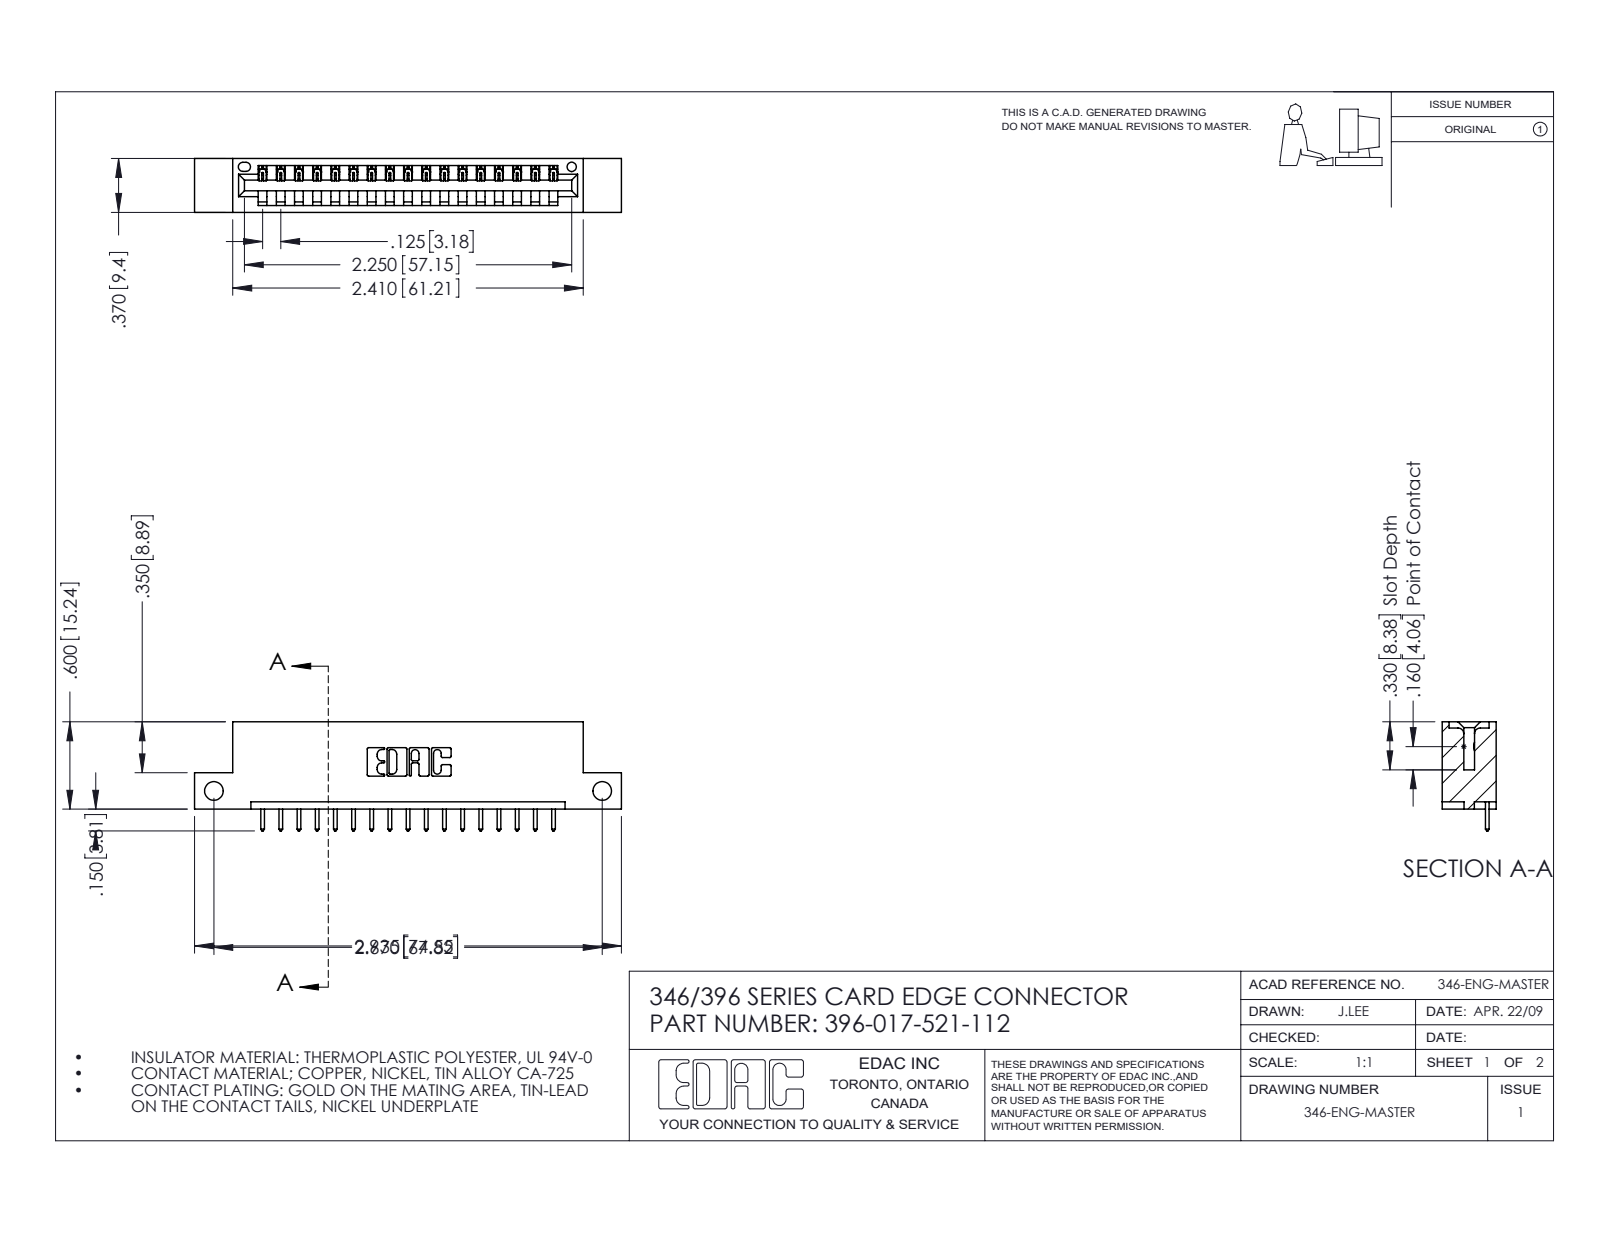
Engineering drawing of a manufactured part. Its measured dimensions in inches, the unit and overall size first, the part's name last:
Units: inches
Overall size (bounding box): 2.935 × 0.75 × 0.37
Round holes (diameter × count): ⌀0.128 ×2, ⌀0.064 ×1
Partial cylindrical surfaces — rounded edges, fillets, slot ends (radius × count): R0.006 ×34, R0.01 ×34, R0.01 ×22, R0.007 ×6, R0.031 ×6, R0.026 ×3, R0.031 ×2, R0.04 ×2
Main face-to-face distances: 0.048, 0.322, 0.25, 0.37, 0.072, 0.298, 0.025, 0.148, 0.222, 0.1
Hole centre spacings: 2.67
Volume: 0.417 in³ · Surface area: 12.29 in²
Bodies: 18 solids, 1108 faces (756 planar, 352 cylindrical, 0 other)
Part name (STEP PRODUCT): 345-292-001_345-293-121; 346 Part_Flush Mounting Lugs - Side Mount; 396-017-521-112
STEP written by: SolidWorks 2016 (CONFIG_CONTROL_DESIGN)
